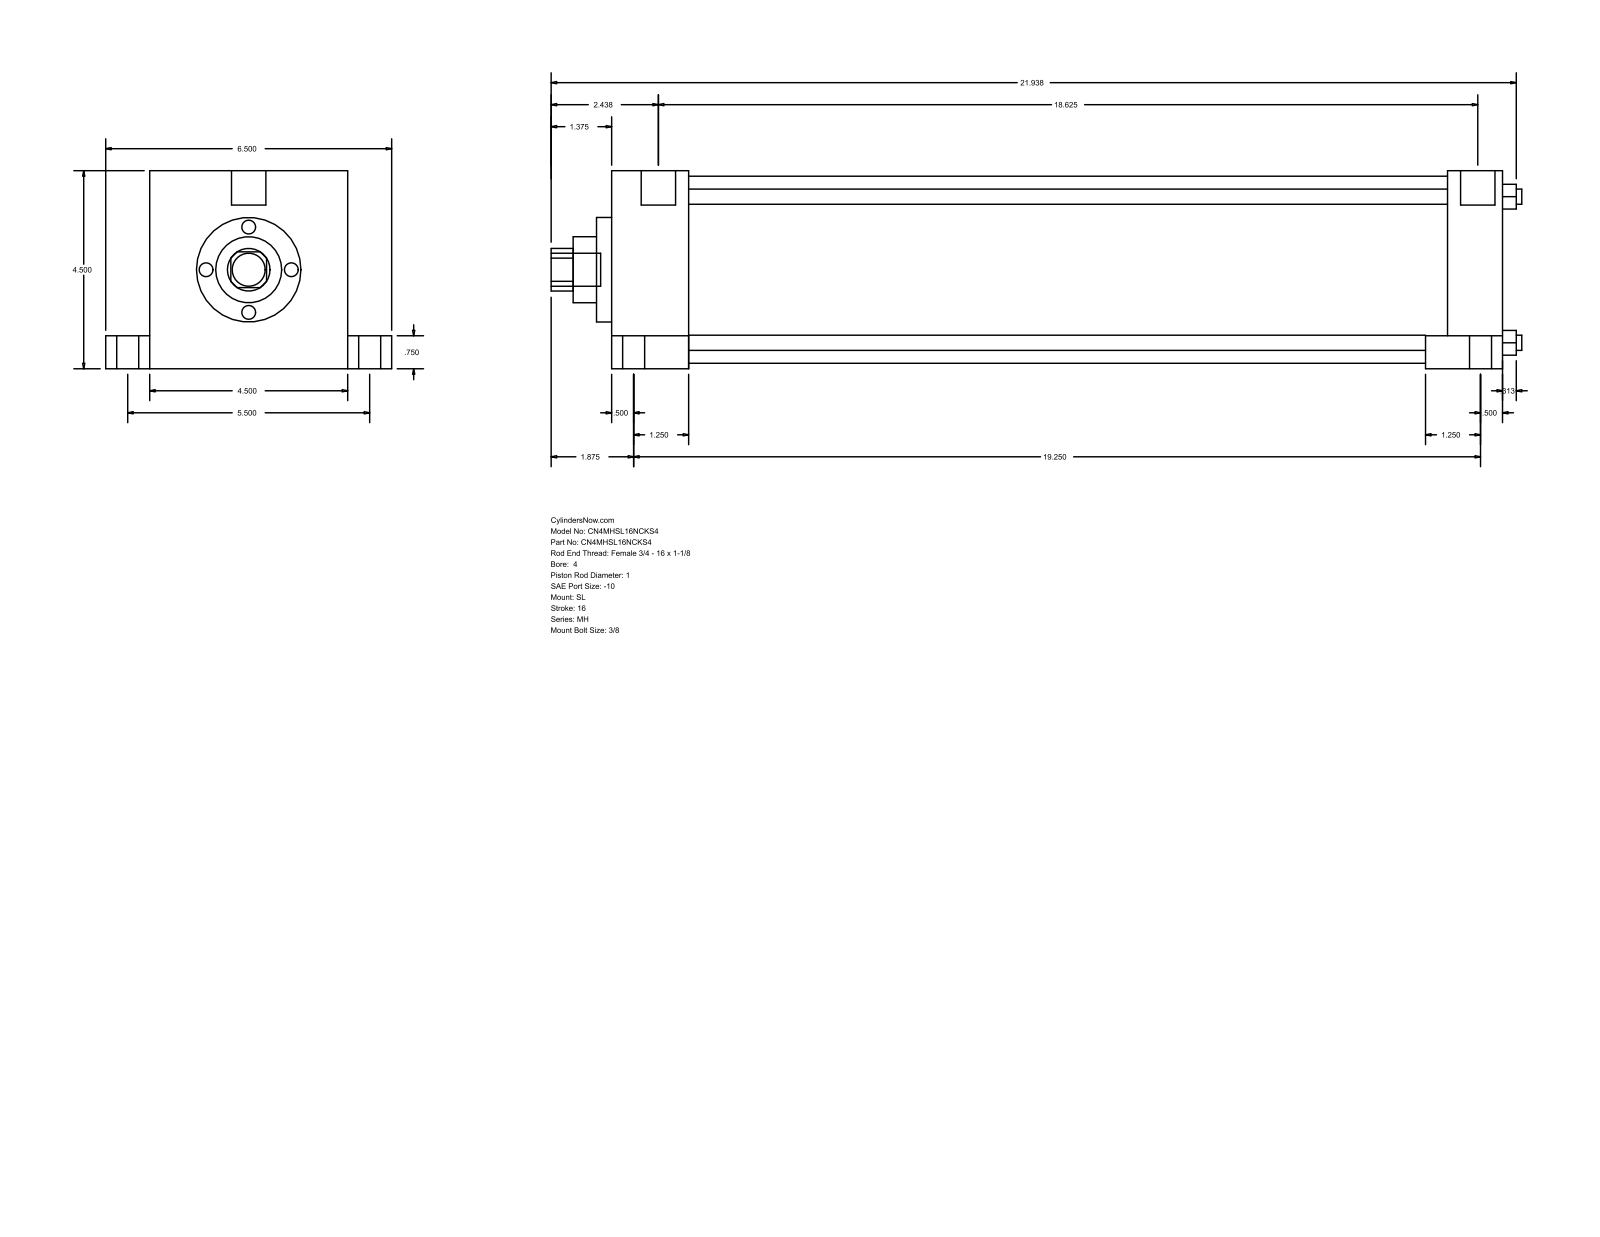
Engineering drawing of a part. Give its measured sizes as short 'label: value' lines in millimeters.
name: MH_SL__0400_1
written by: GSSL Pune (CONFIG_CONTROL_DESIGN)
unit: mm
bodies: 0 solids, 110 faces (77 planar, 33 cylindrical, 0 other)
size: 560.39 × 165.1 × 114.3
holes: 4× ⌀8.76, 1× ⌀25.4, 1× ⌀38.1, 1× ⌀60.33, 1× ⌀107.95
bosses: 5× ⌀19.05, 4× ⌀12.7, 4× ⌀8.73, 2× ⌀19.84
rounds: 1× R12.29
face distances: 114.3, 514.35, 44.46, 469.89, 482.6, 438.14, 31.75, 25.4, 139.7, 19.05
hole spacings: 59.62, 84.32, 119.25
